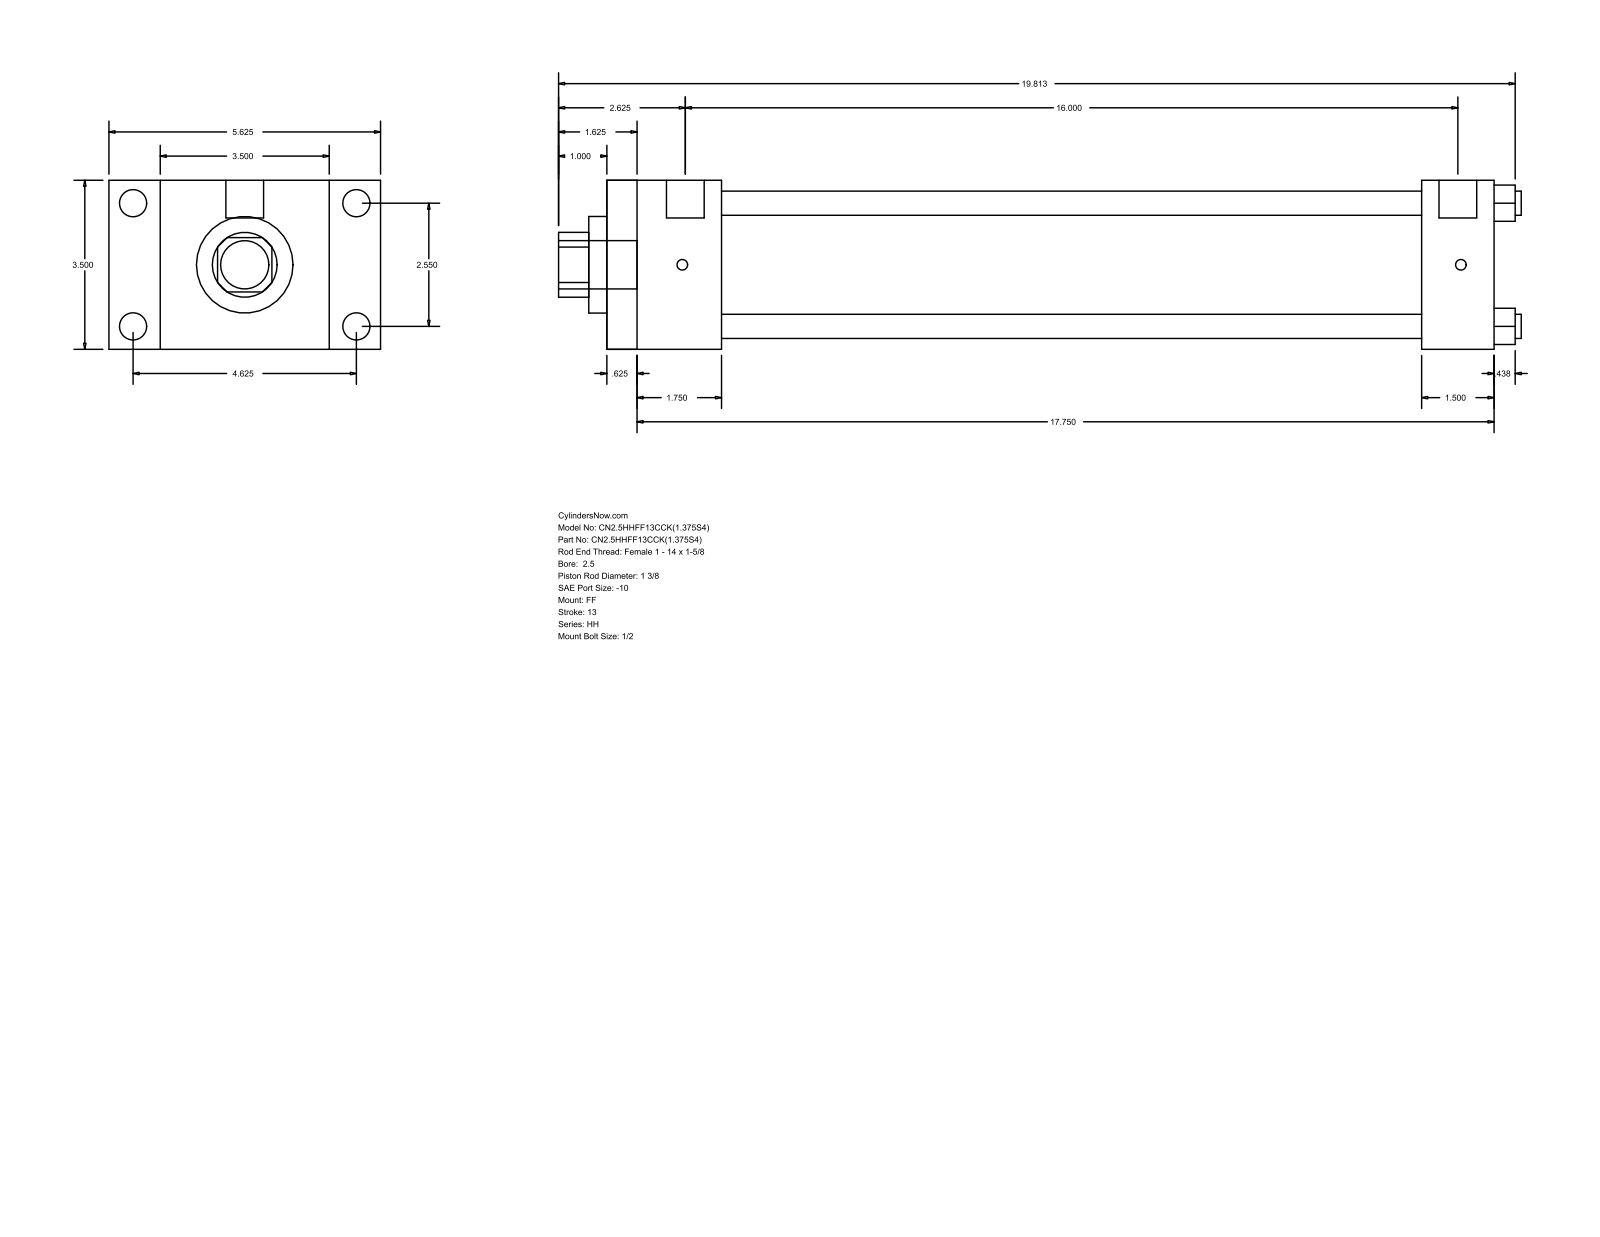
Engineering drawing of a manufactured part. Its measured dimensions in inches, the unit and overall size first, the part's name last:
Units: inches
Overall size (bounding box): 19.937 × 5.625 × 3.5
Round holes (diameter × count): ⌀0.5 ×4, ⌀1.375 ×1, ⌀2 ×1, ⌀2.875 ×1
Round bosses / shafts (diameter × count): ⌀0.563 ×4, ⌀0.219 ×4, ⌀0.781 ×2, ⌀1 ×1
Partial cylindrical surfaces — rounded edges, fillets, slot ends (radius × count): R0.672 ×1
Main face-to-face distances: 3.5, 18.375, 0.625, 17.75, 2.375, 1.75, 16, 16.875, 16.25, 14.5
Hole centre spacings: 1.803, 2.55, 3.606
Bodies: 0 solids, 92 faces (64 planar, 28 cylindrical, 0 other)
Part name (STEP PRODUCT): HH_FF__0250_1.375
STEP written by: GSSL Pune (CONFIG_CONTROL_DESIGN)
